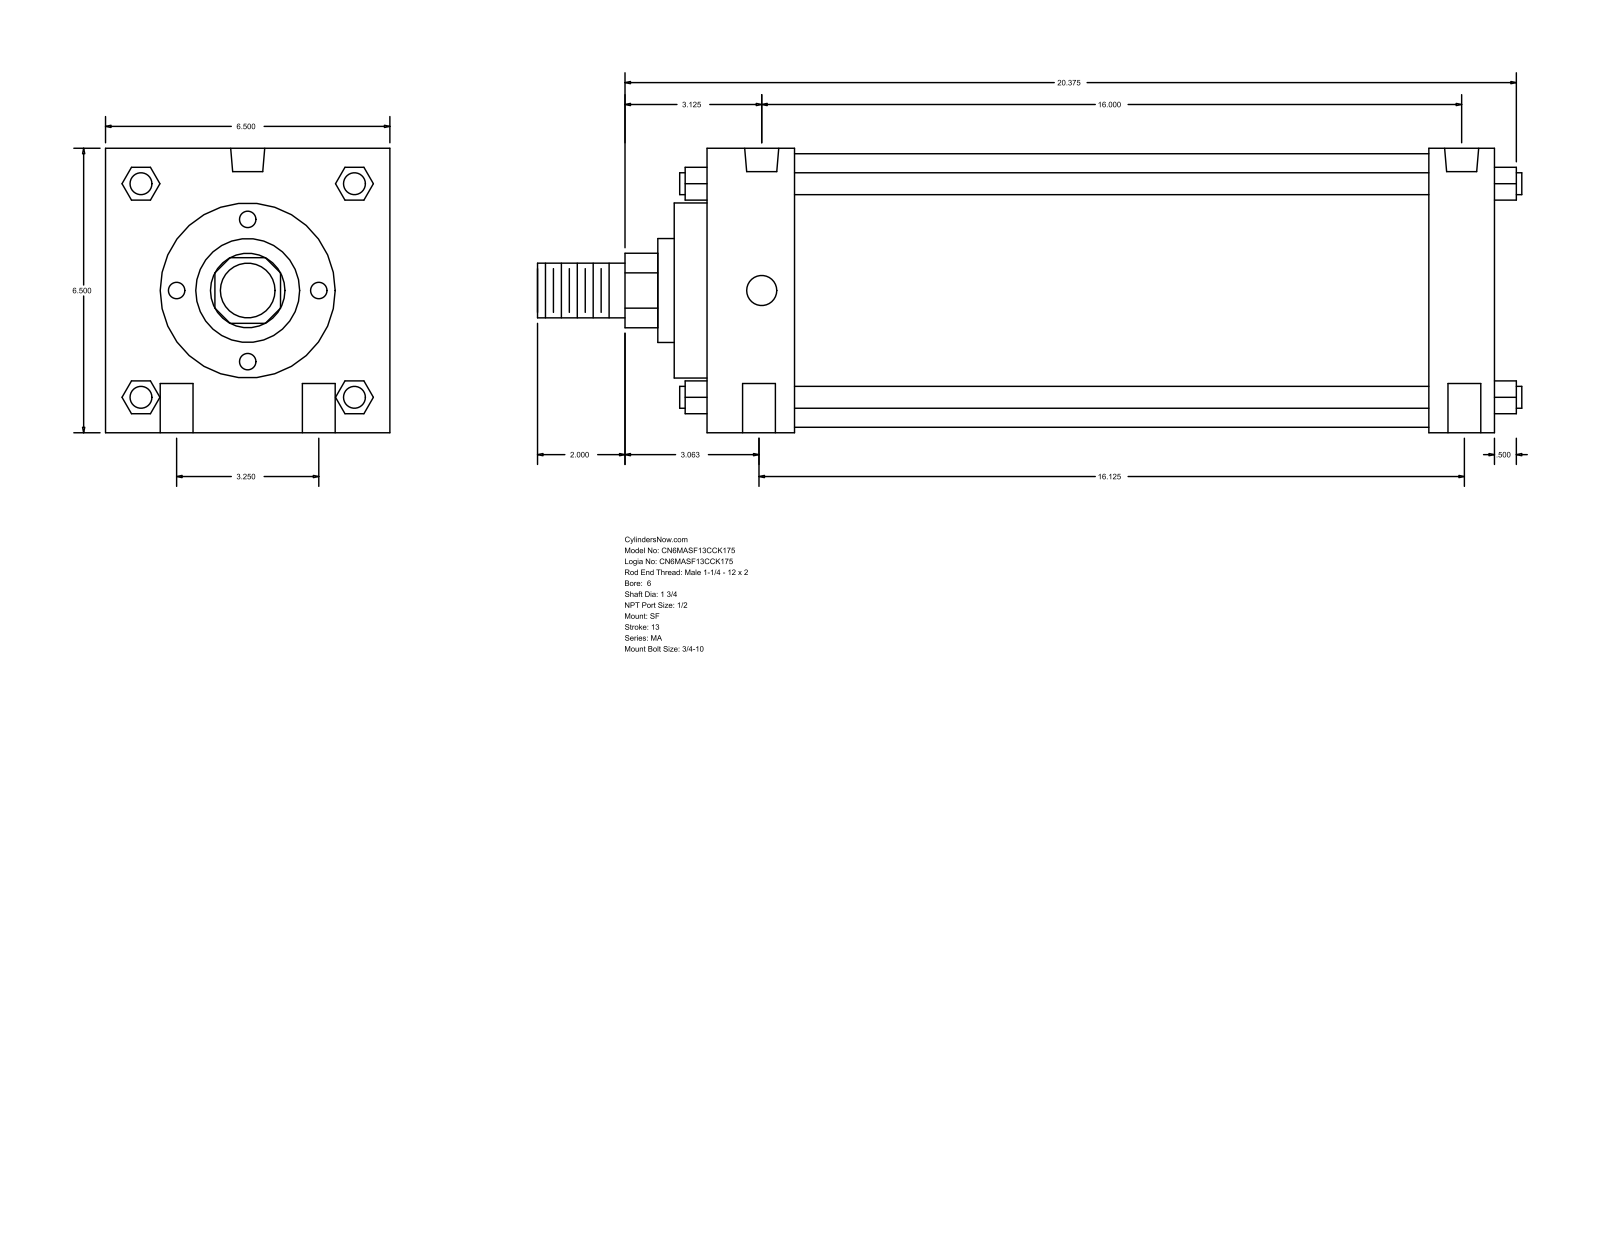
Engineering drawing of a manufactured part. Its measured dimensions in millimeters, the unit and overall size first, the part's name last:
Units: millimetres
Overall size (bounding box): 571.5 × 165.1 × 165.1
Round holes (diameter × count): ⌀19.05 ×4, ⌀17.46 ×2, ⌀19.77 ×2
Round bosses / shafts (diameter × count): ⌀12.7 ×4, ⌀158.75 ×1, ⌀101.6 ×1, ⌀60.33 ×1, ⌀44.45 ×1, ⌀31.75 ×1
Partial cylindrical surfaces — rounded edges, fillets, slot ends (radius × count): R21.63 ×1
Main face-to-face distances: 165.1, 457.2, 19.05, 50.8, 419.11, 38.09, 368.31, 406.4, 69.85, 438.16
Hole centre spacings: 41.3, 410.06, 82.54, 406.39, 409.57, 417.8
Bodies: 0 solids, 126 faces (95 planar, 31 cylindrical, 0 other)
Part name (STEP PRODUCT): MA_SF__0600_1.75
STEP written by: GSSL Pune (CONFIG_CONTROL_DESIGN)
